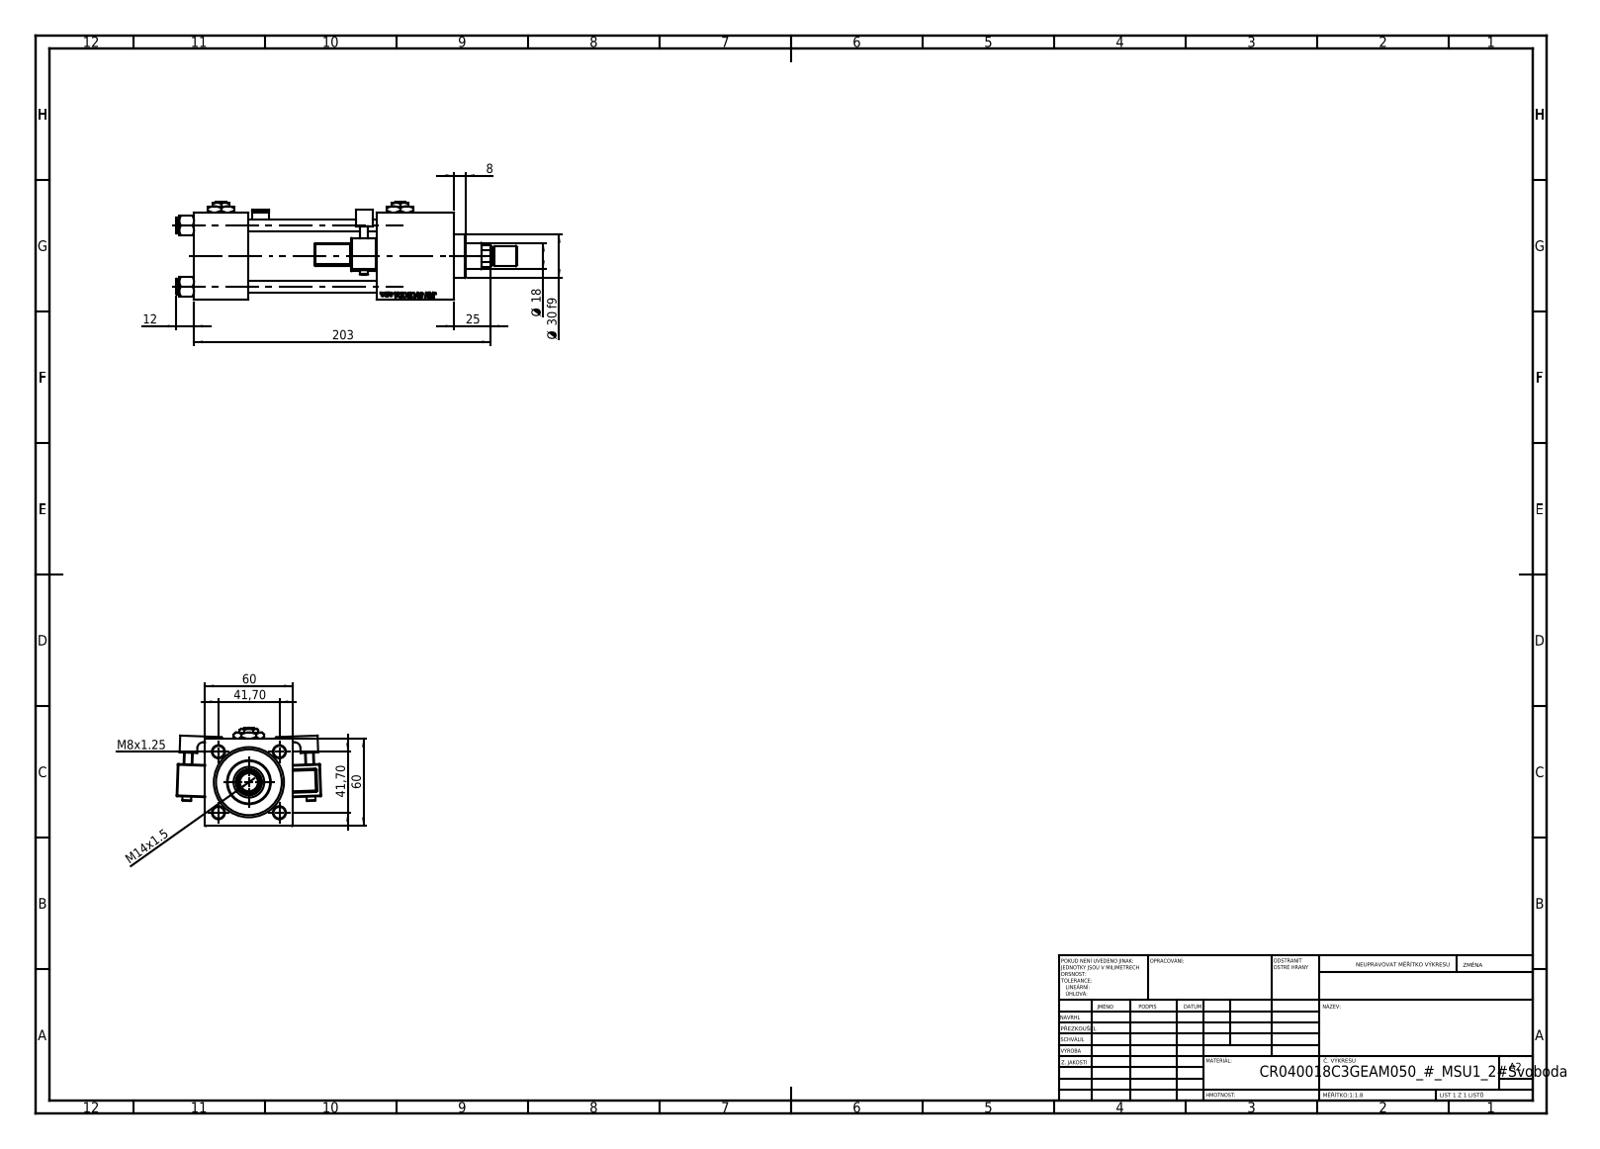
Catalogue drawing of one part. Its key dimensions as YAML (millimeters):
part_name: "Zatka_pro_OIL_PORT; V215CR_C_Body; V215_VC_A; NUT_M5_C (+4 more)"
step_written_by: "SolidWorks 2019 (CONFIG_CONTROL_DESIGN)"
units: millimeters
bodies: {solids: 16, faces: 1418, planar: 636, cylindrical: 162, other: 620}
overall_size: [233, 98.85, 67]
volume: 468173
surface_area: 134366
round_holes:
  - {diameter: 8, count: 4}
  - {diameter: 7, count: 2}
  - {diameter: 16.66, count: 2}
  - {diameter: 24, count: 2}
  - {diameter: 8.5, count: 1}
  - {diameter: 18, count: 1}
  - {diameter: 21, count: 1}
  - {diameter: 31, count: 1}
  - {diameter: 40, count: 1}
  - {diameter: 45, count: 1}
round_bosses_or_shafts:
  - {diameter: 11, count: 4}
  - {diameter: 6, count: 2}
  - {diameter: 46, count: 1}
  - {diameter: 30, count: 1}
  - {diameter: 14, count: 1}
  - {diameter: 12, count: 1}
partial_cylinders:
  - {radius: 0.5, count: 48}
  - {radius: 1, count: 2}
  - {radius: 2.5, count: 2}
  - {radius: 4, count: 2}
  - {radius: 8.5, count: 1}
face_to_face_distances: [60, 37, 125, 88, 53, 178, 141, 149.3, 112.3, 24.3]
hole_center_spacings: [29.49, 41.7, 58.97, 122.5]
